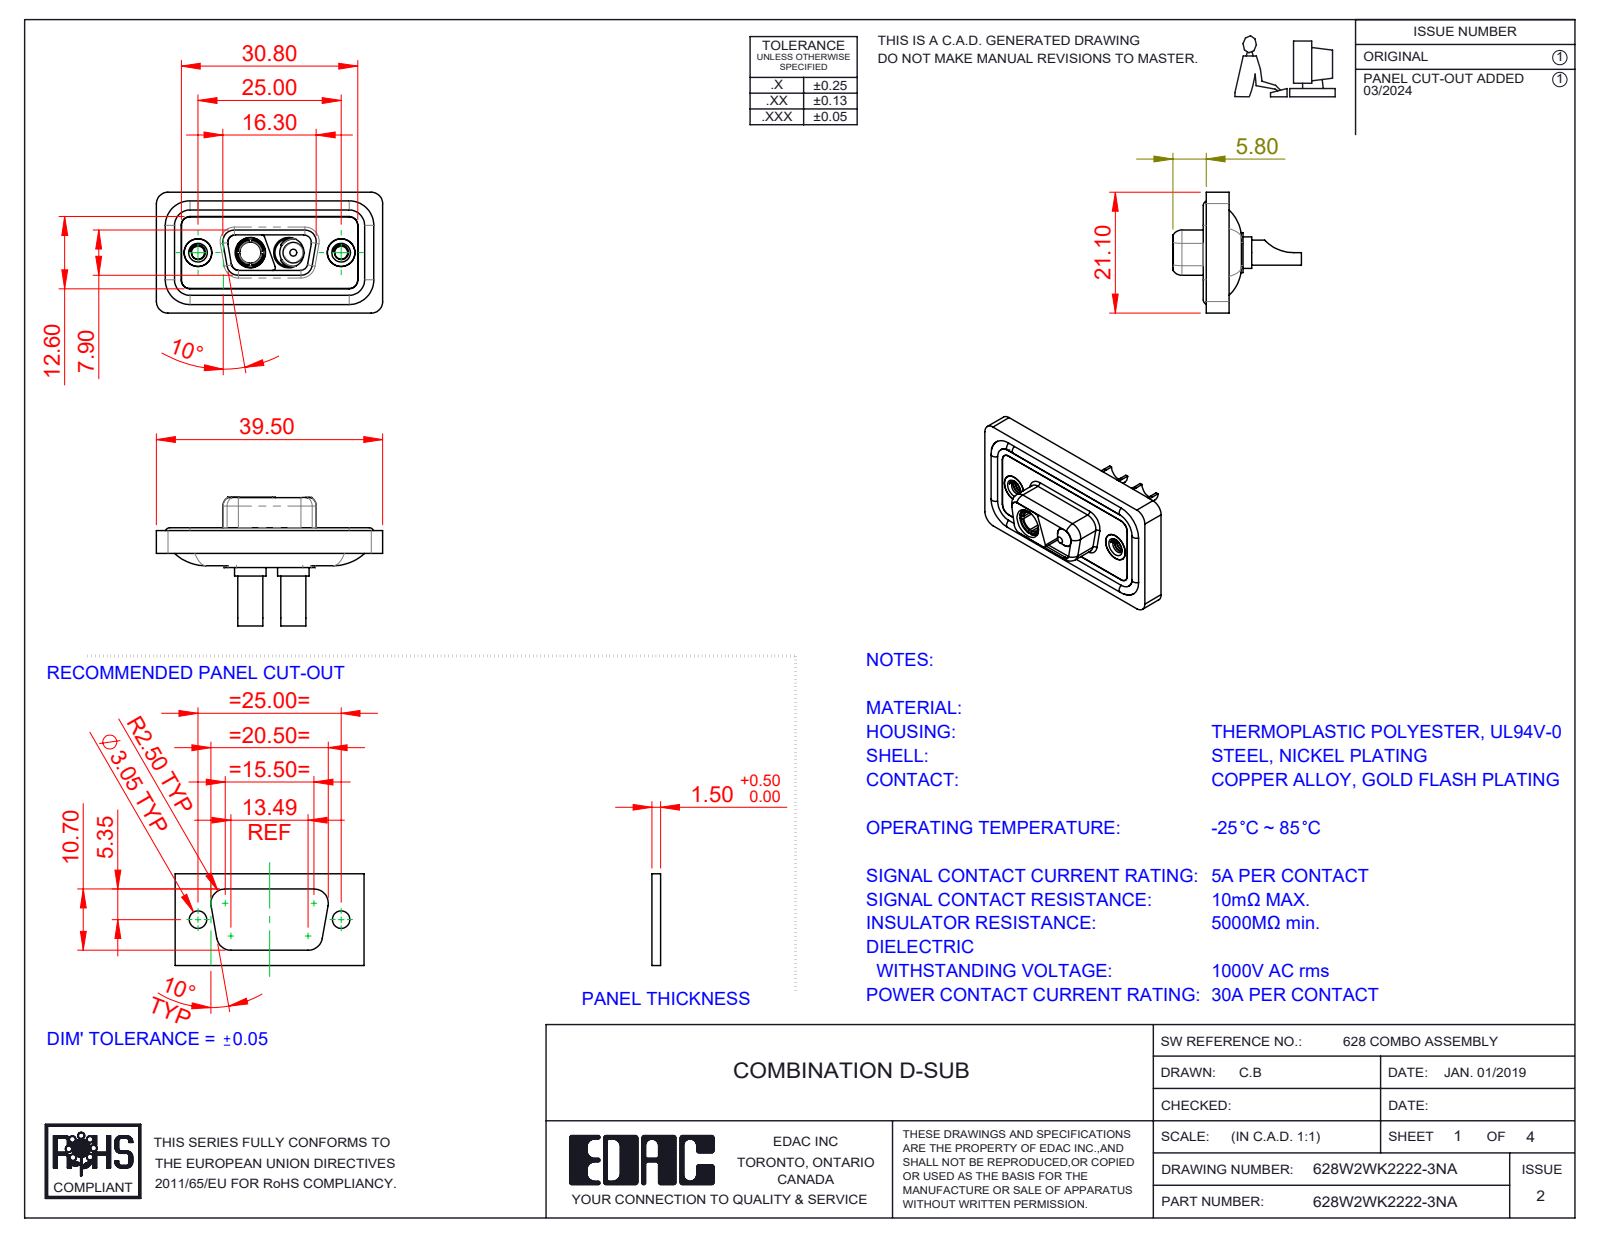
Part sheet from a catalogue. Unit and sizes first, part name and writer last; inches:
Units: inches
Overall size (bounding box): 1.555 × 0.884 × 0.831
Round holes (diameter × count): ⌀0.191 ×4, ⌀0.089 ×2, ⌀0.138 ×2, ⌀0.157 ×2, ⌀0.159 ×2, ⌀0.197 ×2, ⌀0.209 ×2, ⌀0.146 ×1
Round bosses / shafts (diameter × count): ⌀0.063 ×4, ⌀0.217 ×2, ⌀0.205 ×2, ⌀0.195 ×2, ⌀0.189 ×2, ⌀0.187 ×2, ⌀0.173 ×2, ⌀0.148 ×2
Partial cylindrical surfaces — rounded edges, fillets, slot ends (radius × count): R0.059 ×22, R0.079 ×18, R0.053 ×8, R0.063 ×8, R0.02 ×6, R0.01 ×4, R0.024 ×4, R0.026 ×4
Main face-to-face distances: 0.016, 0.043, 0.114, 0.063, 0.02, 0.071, 0.222, 0.211, 0.122, 0.028
Hole centre spacings: 0.36, 0.624, 0.265, 0.984
Volume: 0.284 in³ · Surface area: 11.71 in²
Bodies: 11 solids, 510 faces (150 planar, 239 cylindrical, 121 other)
Part name (STEP PRODUCT): 628W2WK2222-3NA; 628Combo Threaded Rivet_A; 628Combo Housing_2WK2; 628Combo Shell Front_09 Contacts (+4 more)
STEP written by: SolidWorks 2023 (CONFIG_CONTROL_DESIGN)
